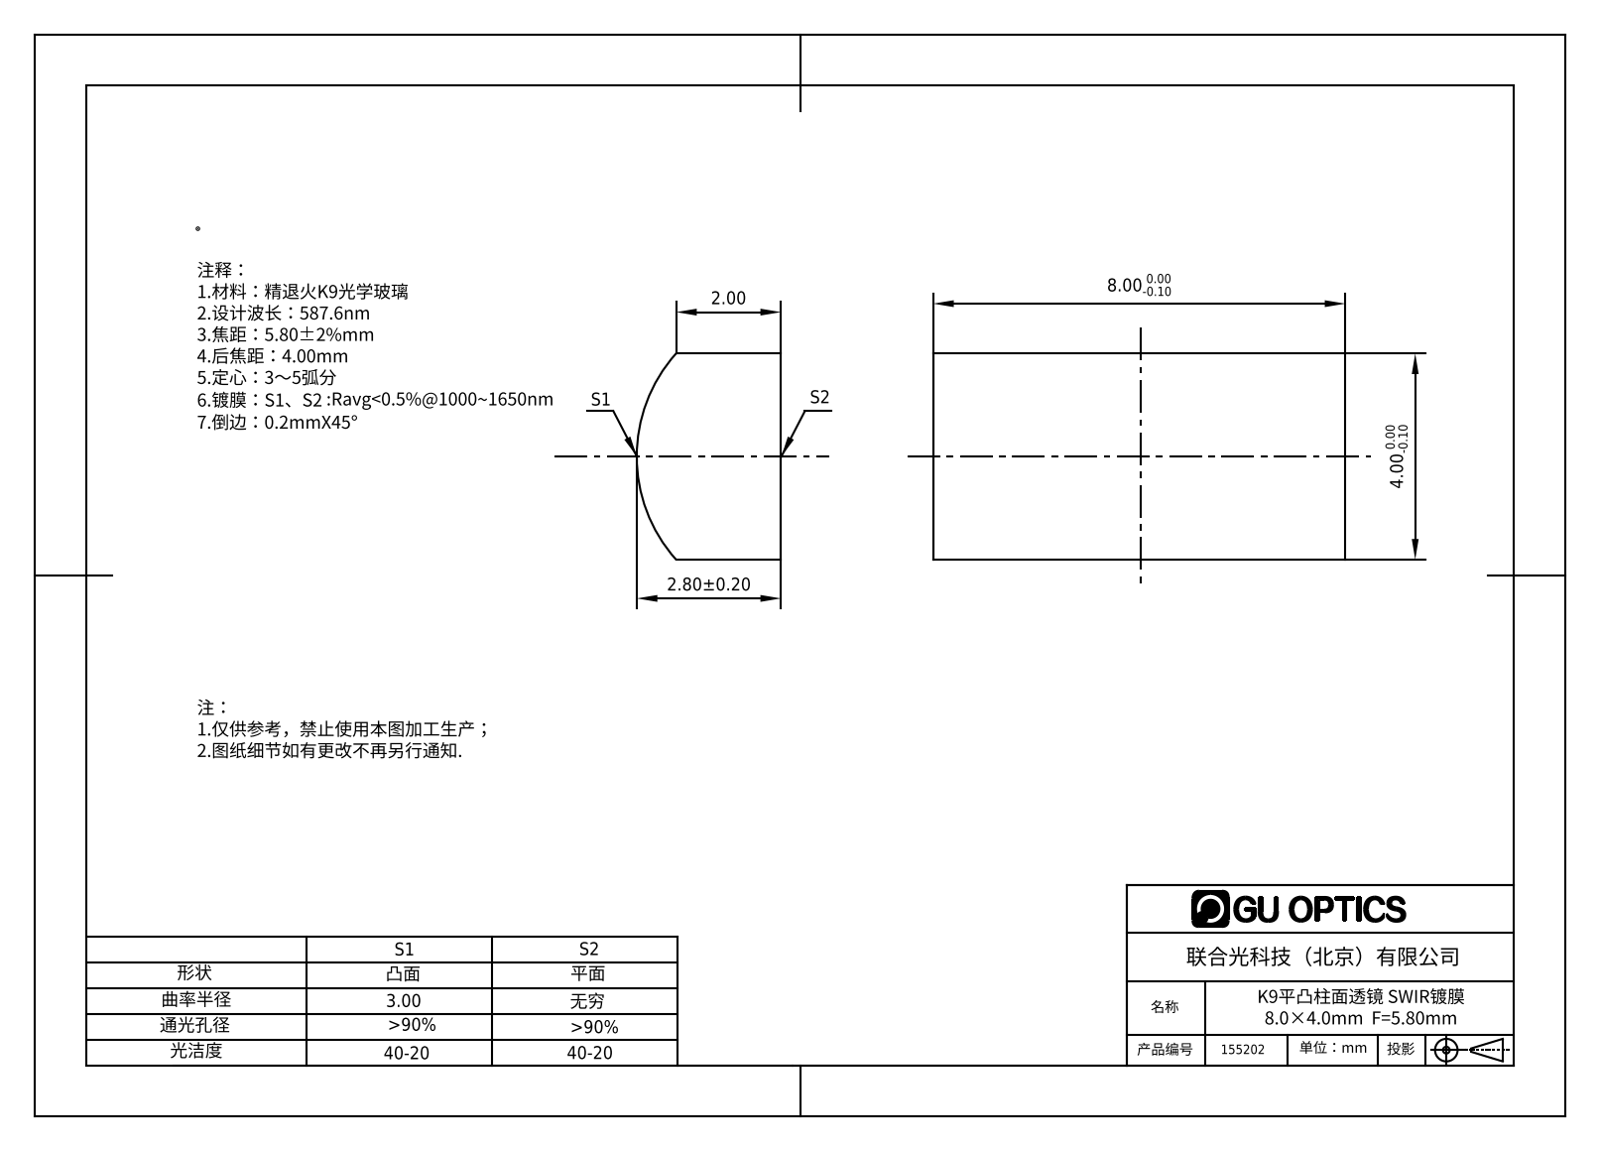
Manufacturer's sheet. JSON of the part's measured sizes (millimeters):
{"part_name": "155004", "step_written_by": "SolidWorks 2016 (AUTOMOTIVE_DESIGN)", "units": "millimeters", "bodies": {"solids": 1, "faces": 6, "planar": 5, "cylindrical": 1, "other": 0}, "overall_size": [8, 4, 2.8], "volume_mm3": 82, "surface_area_mm2": 120, "partial_cylinders_radius": [[3, 1]], "face_to_face_distances": [4, 8]}
